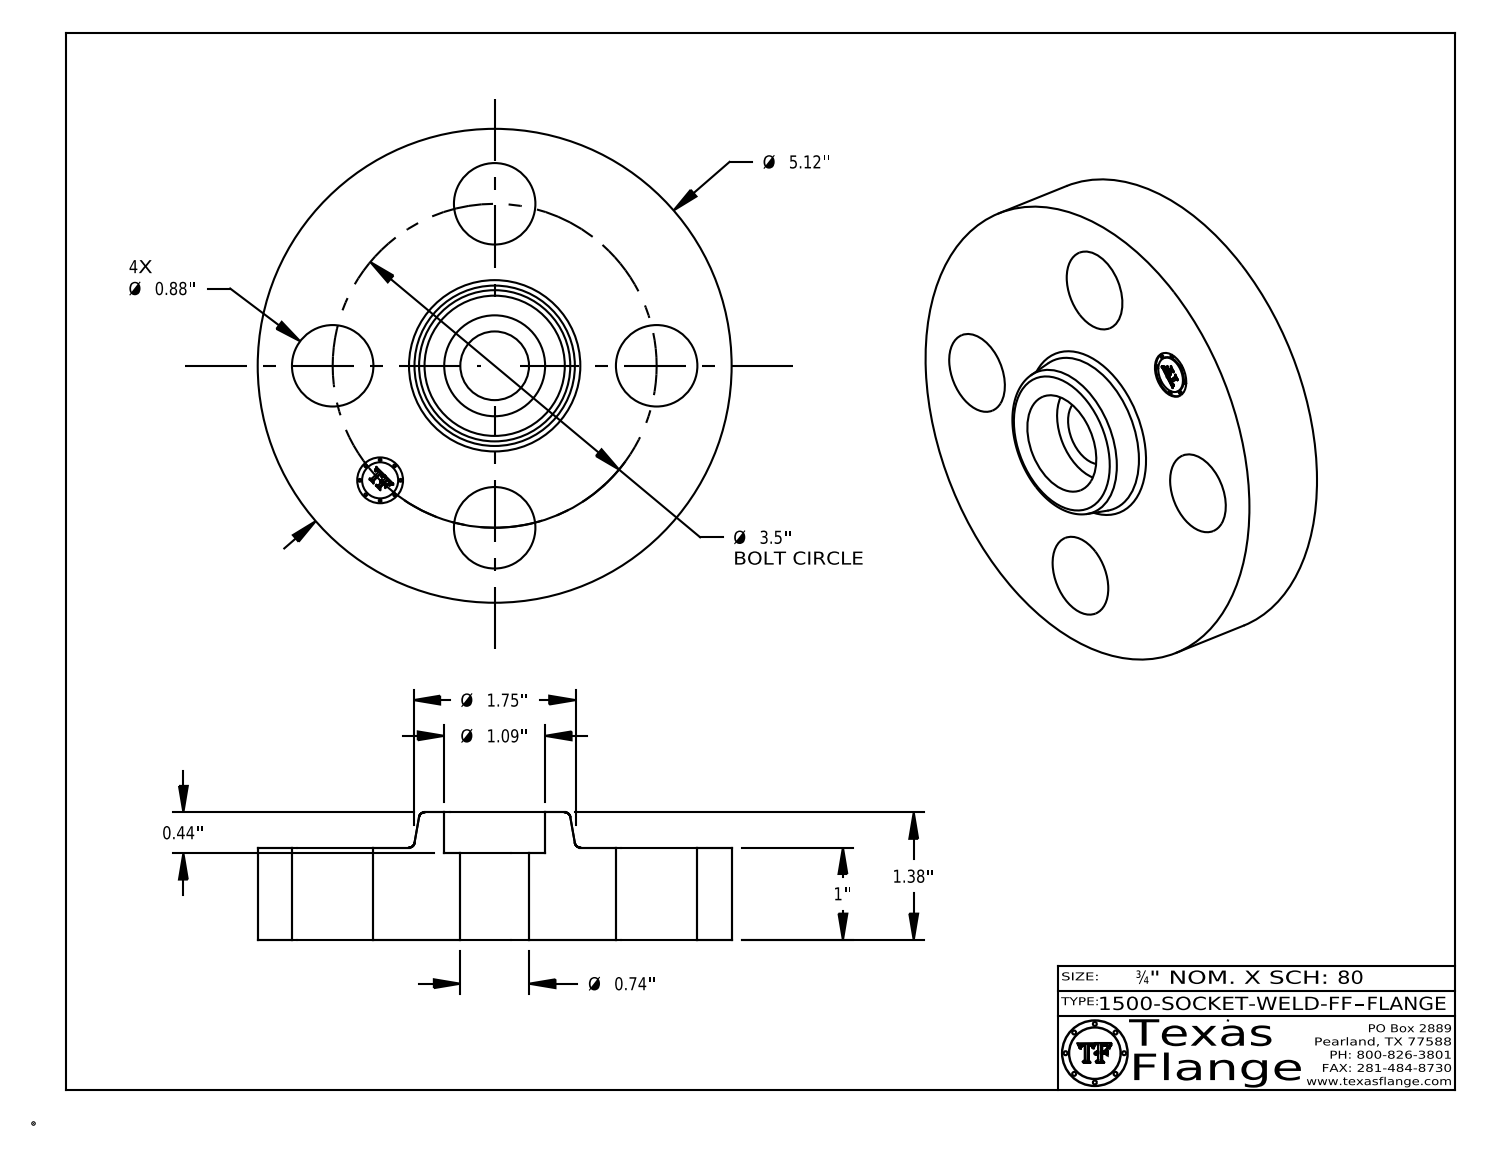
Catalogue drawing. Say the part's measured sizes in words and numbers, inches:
The part is named "1500-SOCKET-WELD-FF". Its 3-D file was written by "CATIA V5 STEP AP214 (AUTOMOTIVE_DESIGN)". It is 1 solid with 409 faces: 369 planar, 34 cylindrical and 6 other. Overall it measures 5.12 by 5.12 by 1.38 inches. Its volume is 18.18 cubic inches and its surface area 67.89 square inches. Round holes: 4 of diameter 0.88, 1 of diameter 0.495, 1 of diameter 0.742, 1 of diameter 1.09. Round bosses or shafts: 8 of diameter 0.03, 1 of diameter 5.12, 1 of diameter 0.39. The main face-to-face distances are 1, 1.38, 0.38, 0.06, 0.94, 0.44, 0.015, 0.985, 0.045, 0.395. The hole center spacings are 1.75, 2.475, 1.339, 3.233, 3.5.
